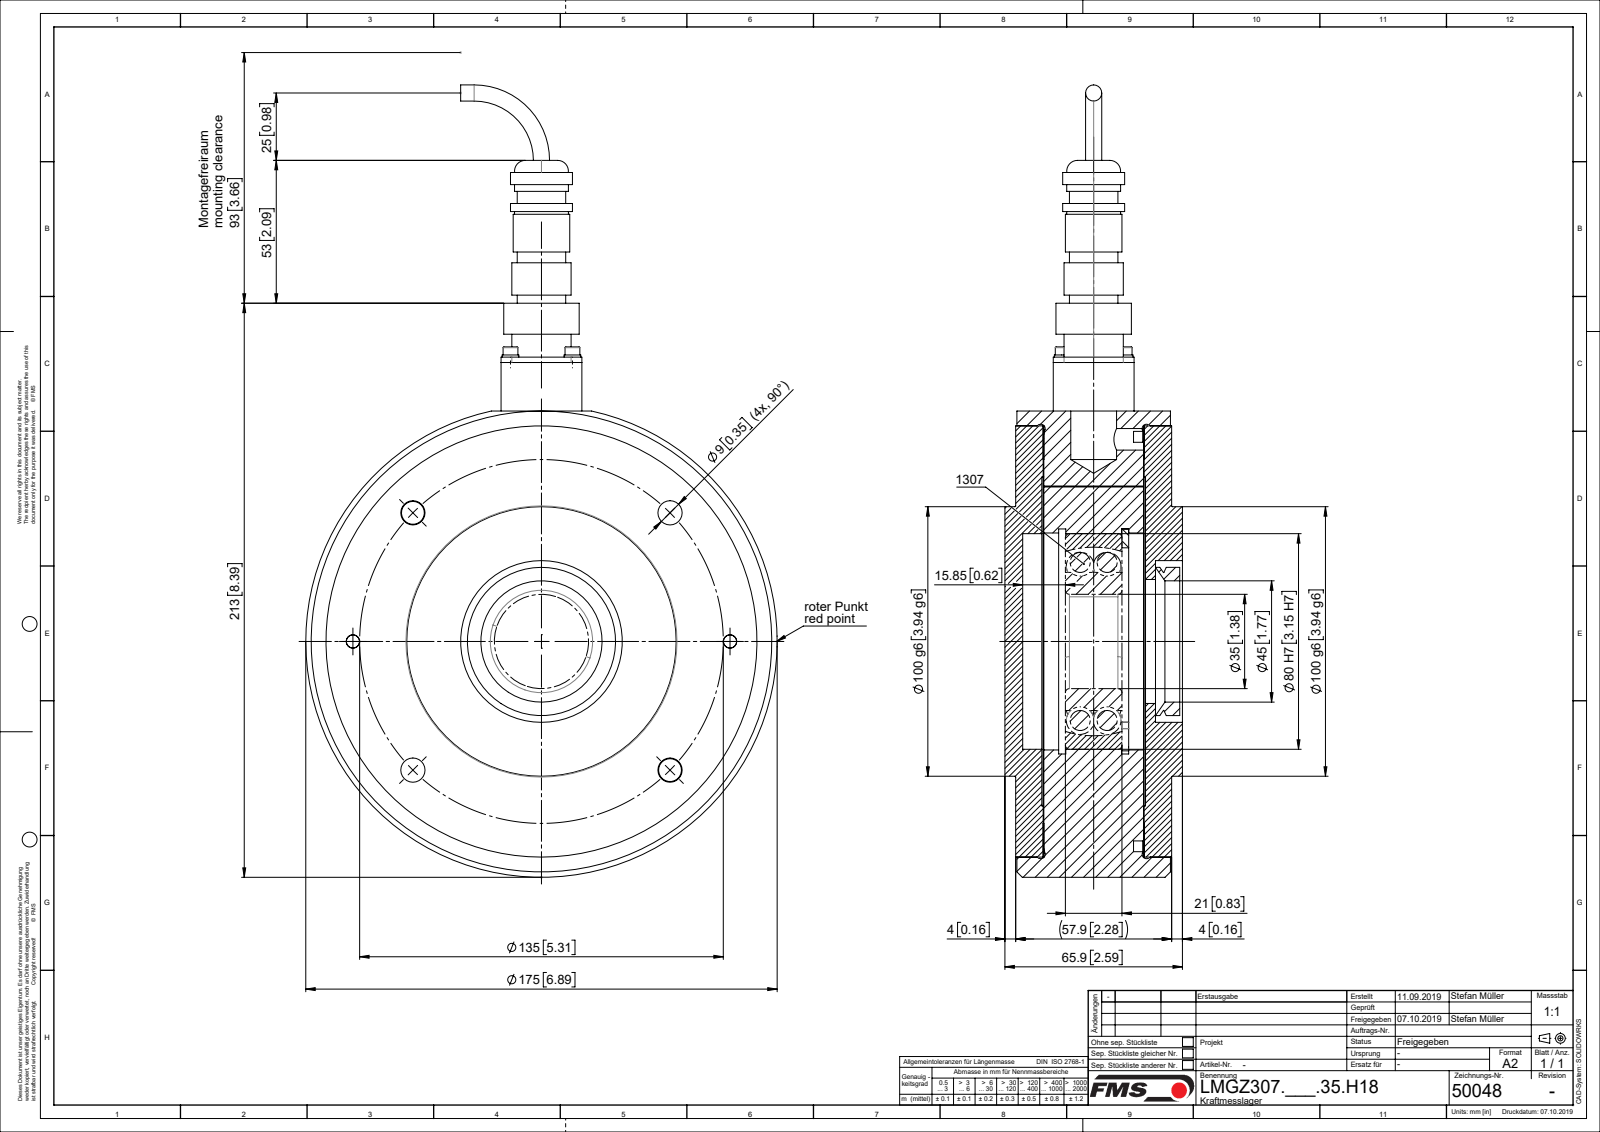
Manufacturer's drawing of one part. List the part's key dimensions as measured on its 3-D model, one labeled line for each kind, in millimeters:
Part name (STEP PRODUCT): L50048; L4857104; TEIL1; L48573 (+8 more)
STEP written by: Mechanical Desktop 2007 (CONFIG_CONTROL_DESIGN)
Units: millimetres
Bodies: 20 solids, 368 faces (87 planar, 227 cylindrical, 54 other)
Overall size (bounding box): 317.5 × 294 × 104.7
Volume: 1 293 000 mm³ · Surface area: 267 577 mm²
Round holes (diameter × count): ⌀2.6 ×4, ⌀3.2 ×4, ⌀3.4 ×4, ⌀9 ×4, ⌀5 ×2, ⌀6.6 ×2, ⌀8.68 ×2, ⌀11 ×2, ⌀35 ×1, ⌀44 ×1, ⌀46 ×1, ⌀60 ×1
Round bosses / shafts (diameter × count): ⌀6.2 ×4, ⌀5.5 ×4, ⌀3 ×4, ⌀2.5 ×4, ⌀6 ×3, ⌀10 ×2, ⌀175 ×1, ⌀160 ×1
Partial cylindrical surfaces — rounded edges, fillets, slot ends (radius × count): R4 ×4, R7.5 ×2
Main face-to-face distances: 37.25, 10.2, 10.45, 47.45, 47.7, 37, 38, 9.7, 48.2, 0.5
Hole centre spacings: 23, 52.67, 67.5, 95.46, 127.04, 32.53, 70, 135
